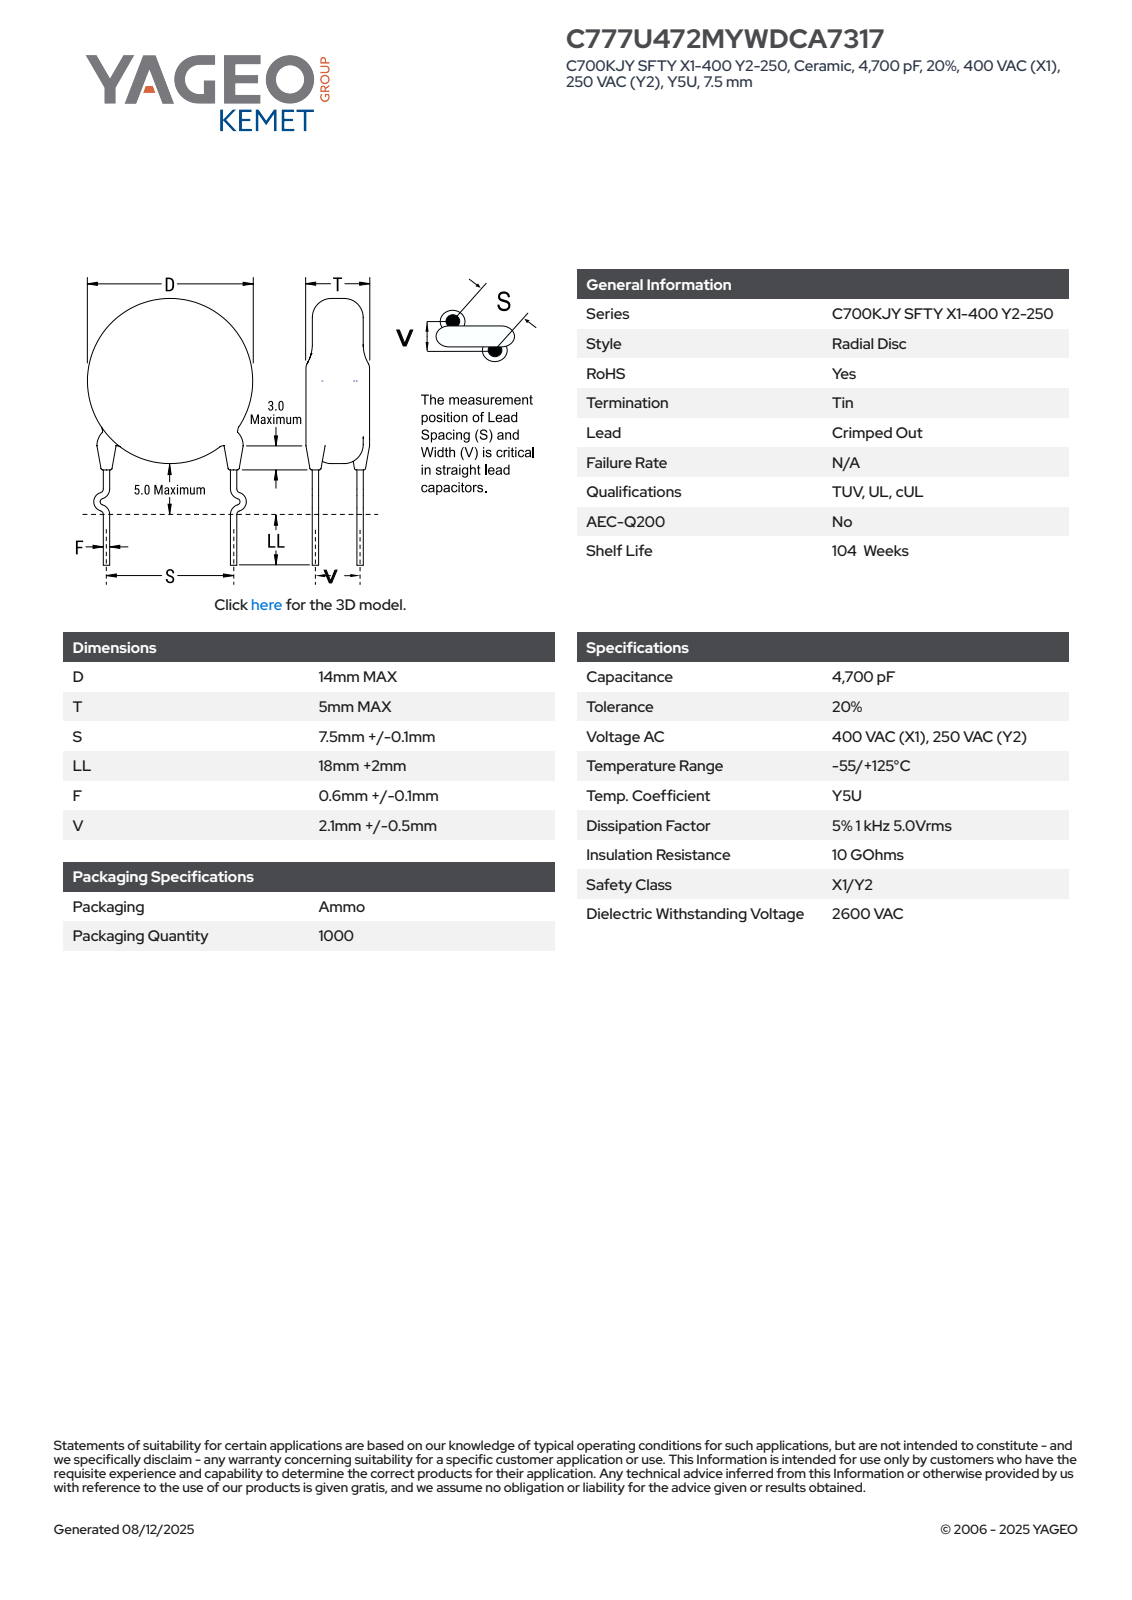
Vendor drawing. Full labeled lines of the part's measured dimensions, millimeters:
Part name (STEP PRODUCT): CCD_KCO_14X5_D14T5S7.5LL20F0.7V2.1
STEP written by: SolidWorks 2021 (AUTOMOTIVE_DESIGN)
Units: millimetres
Bodies: 4 solids, 109 faces (63 planar, 26 cylindrical, 20 other)
Overall size (bounding box): 39.38 × 14 × 5
Volume: 775 mm³ · Surface area: 633 mm²
Round bosses / shafts (diameter × count): ⌀0.7 ×8, ⌀1.2 ×2, ⌀14 ×1
Main face-to-face distances: 5, 25, 33.57, 8.57, 31.93, 6.93, 1.64, 0.31, 1.33, 3.36
